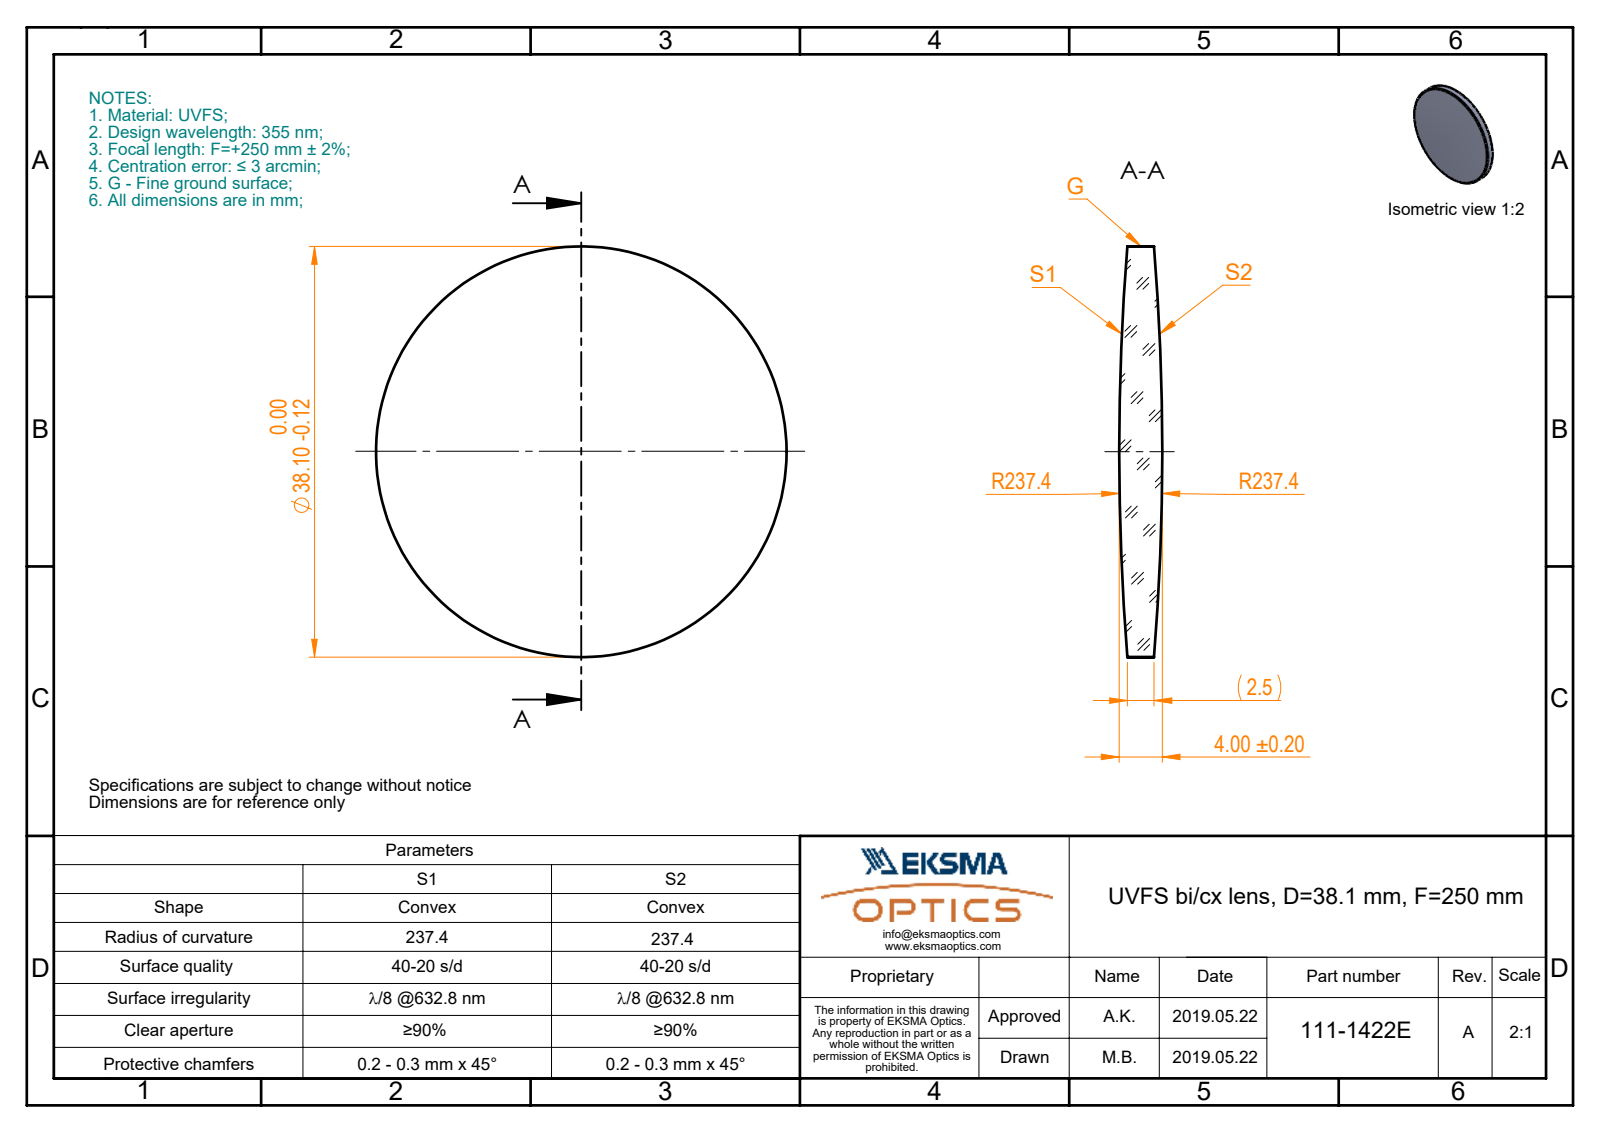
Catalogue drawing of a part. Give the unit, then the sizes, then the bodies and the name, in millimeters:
Units: millimetres
Overall size (bounding box): 38.1 × 38.1 × 4
Round bosses / shafts (diameter × count): ⌀38.1 ×1
Volume: 3 688 mm³ · Surface area: 2 579 mm²
Bodies: 1 solid, 6 faces (0 planar, 2 cylindrical, 4 other)
Part name (STEP PRODUCT): 111-1422E UVFS bi-cx 38.1 F250
STEP written by: SolidWorks 2017 (CONFIG_CONTROL_DESIGN)
